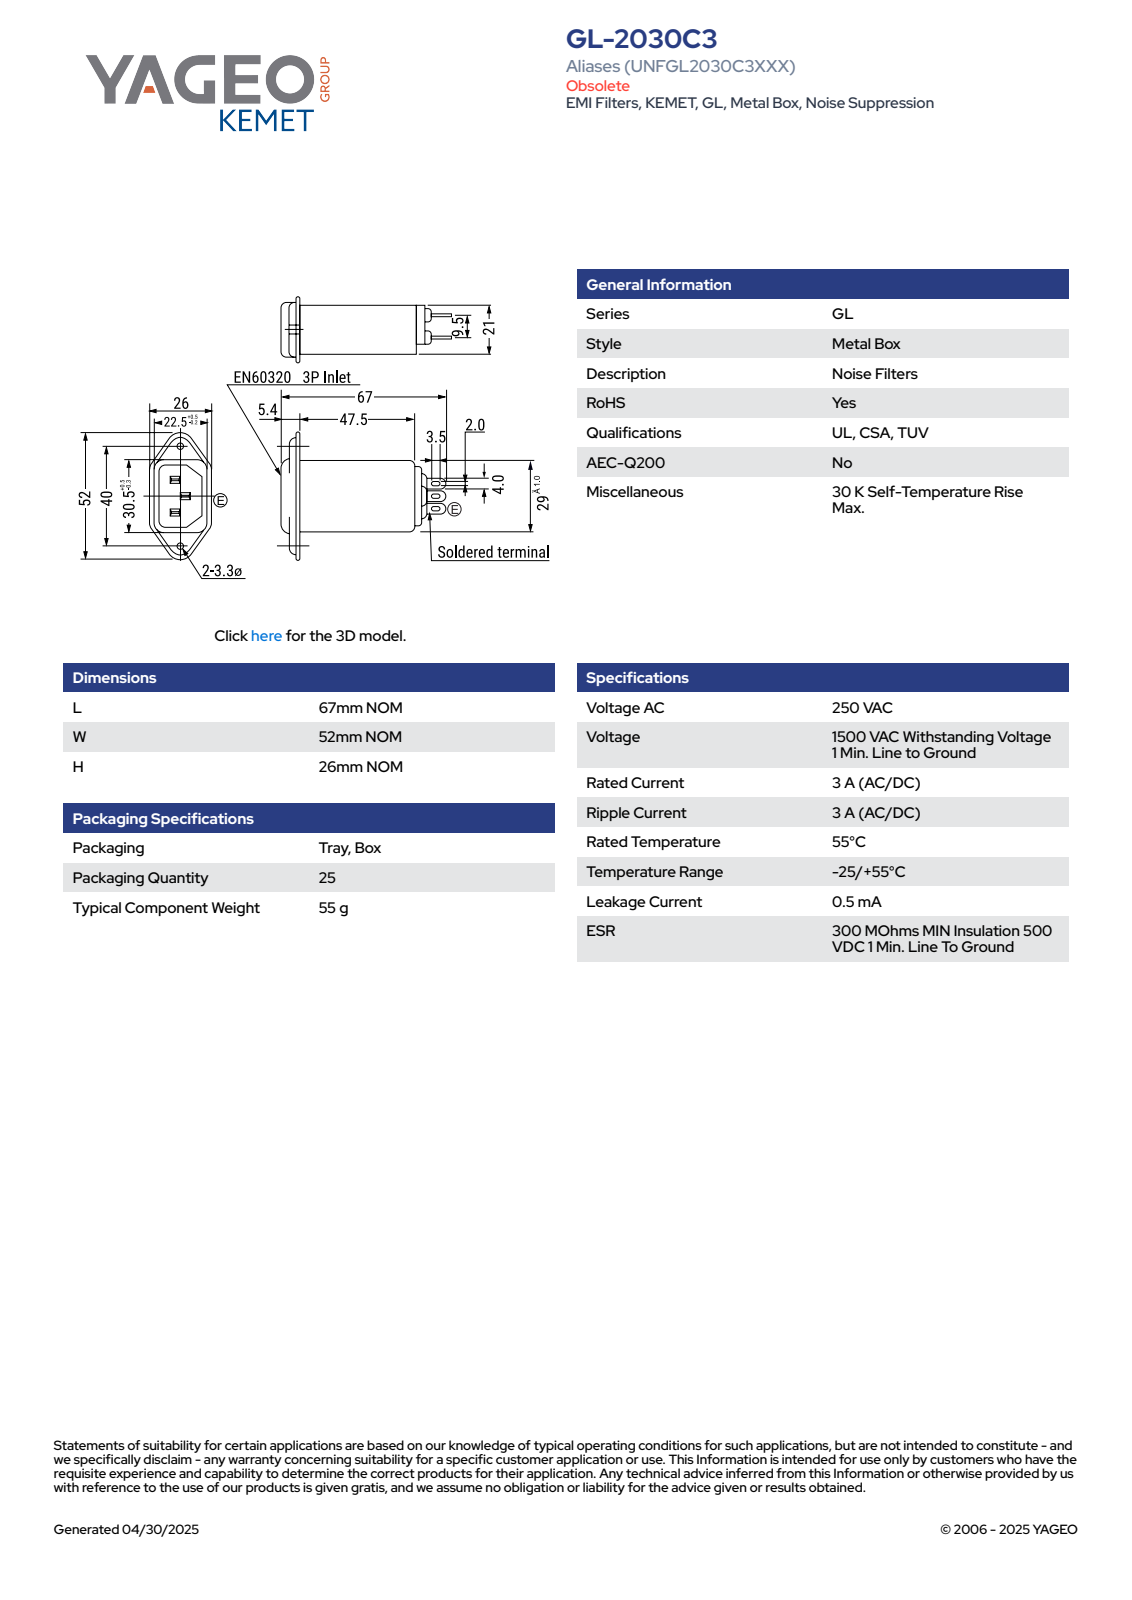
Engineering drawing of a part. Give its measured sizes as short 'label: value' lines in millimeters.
name: ENF_KGLC_L67W52H26
written by: SolidWorks 2014 (AUTOMOTIVE_DESIGN)
unit: mm
bodies: 1 solid, 209 faces (132 planar, 61 cylindrical, 16 other)
size: 67 × 52 × 26
volume: 33 097 mm³; area: 9 188 mm²
holes: 2× ⌀3.3
bosses: 3× ⌀5.2
rounds: 28× R1, 15× R2, 2× R3
face distances: 21, 30, 2, 49.5, 47.5, 2.1, 47.4, 1, 20, 22
hole spacings: 40
